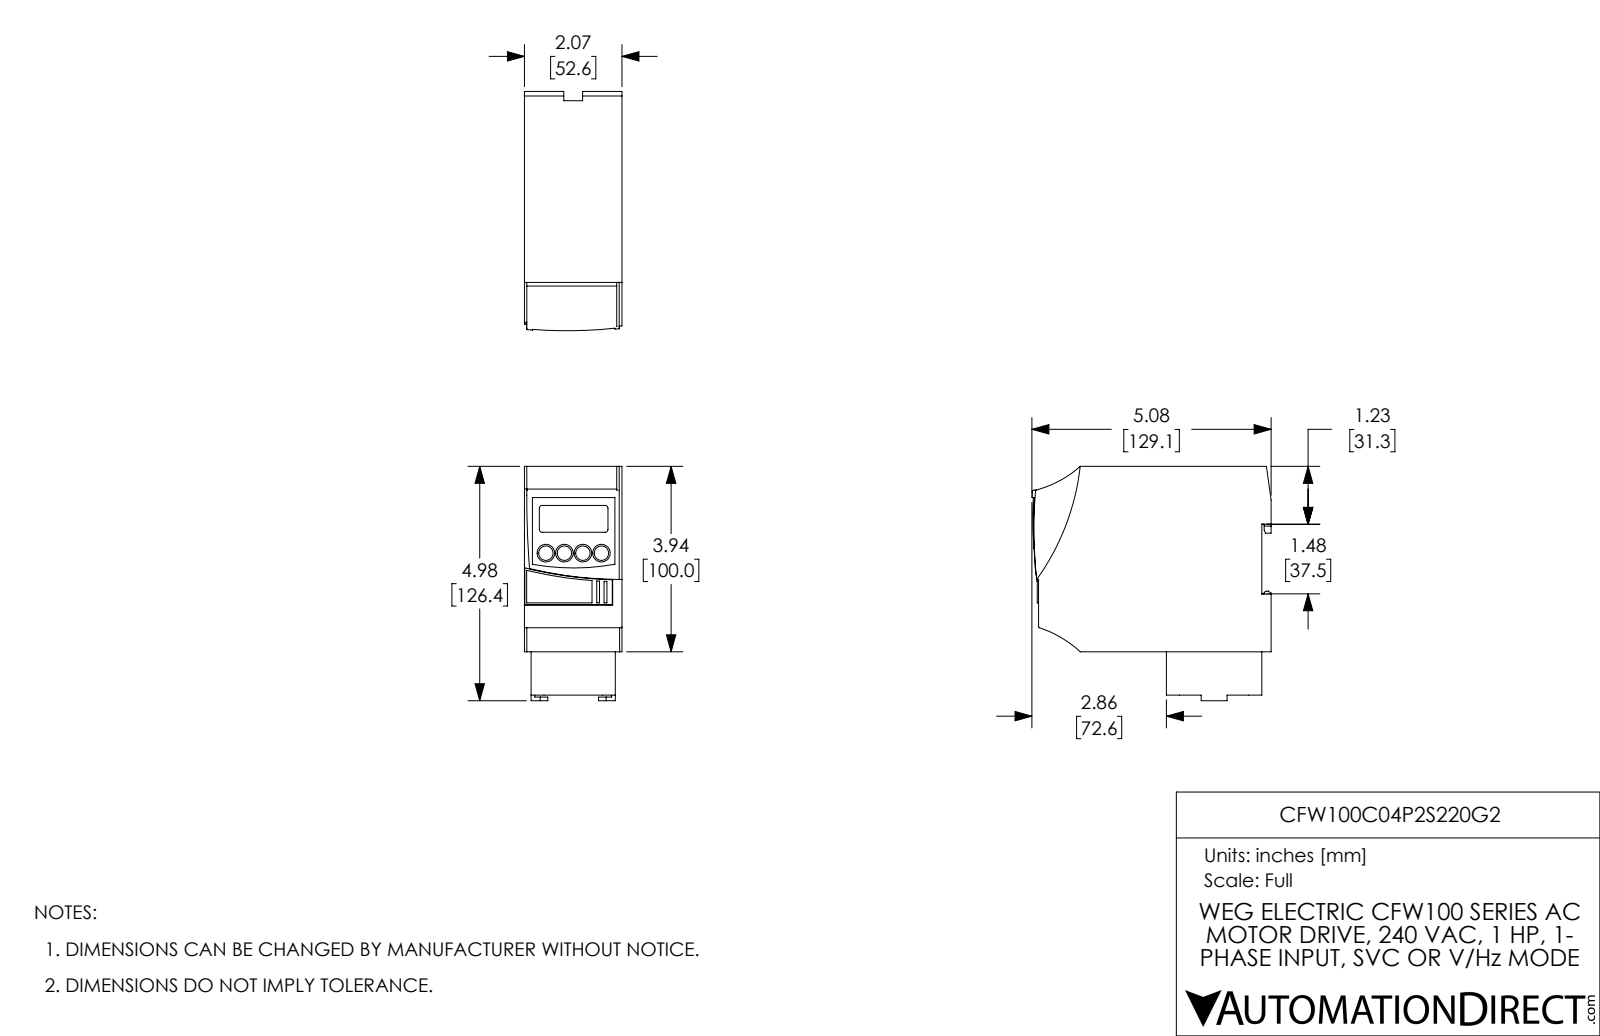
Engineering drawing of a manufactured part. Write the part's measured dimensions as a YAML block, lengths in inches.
part_name: "CFW100C04P2S220G2"
step_written_by: "SolidWorks 2017 (AUTOMOTIVE_DESIGN)"
units: inches
bodies: {solids: 1, faces: 150, planar: 118, cylindrical: 22, other: 10}
overall_size: [5.082, 4.976, 2.073]
volume: 41.14
surface_area: 85.16
partial_cylinders:
  - {radius: 0.059, count: 4}
  - {radius: 0.276, count: 4}
  - {radius: 2.362, count: 2}
  - {radius: 0.012, count: 1}
  - {radius: 0.02, count: 1}
  - {radius: 4.912, count: 1}
  - {radius: 5.118, count: 1}
  - {radius: 8.52, count: 1}
face_to_face_distances: [2.072, 3.937, 0.921, 4.858, 0.197, 0.141, 1.932, 4.941, 4.744, 1.431]
